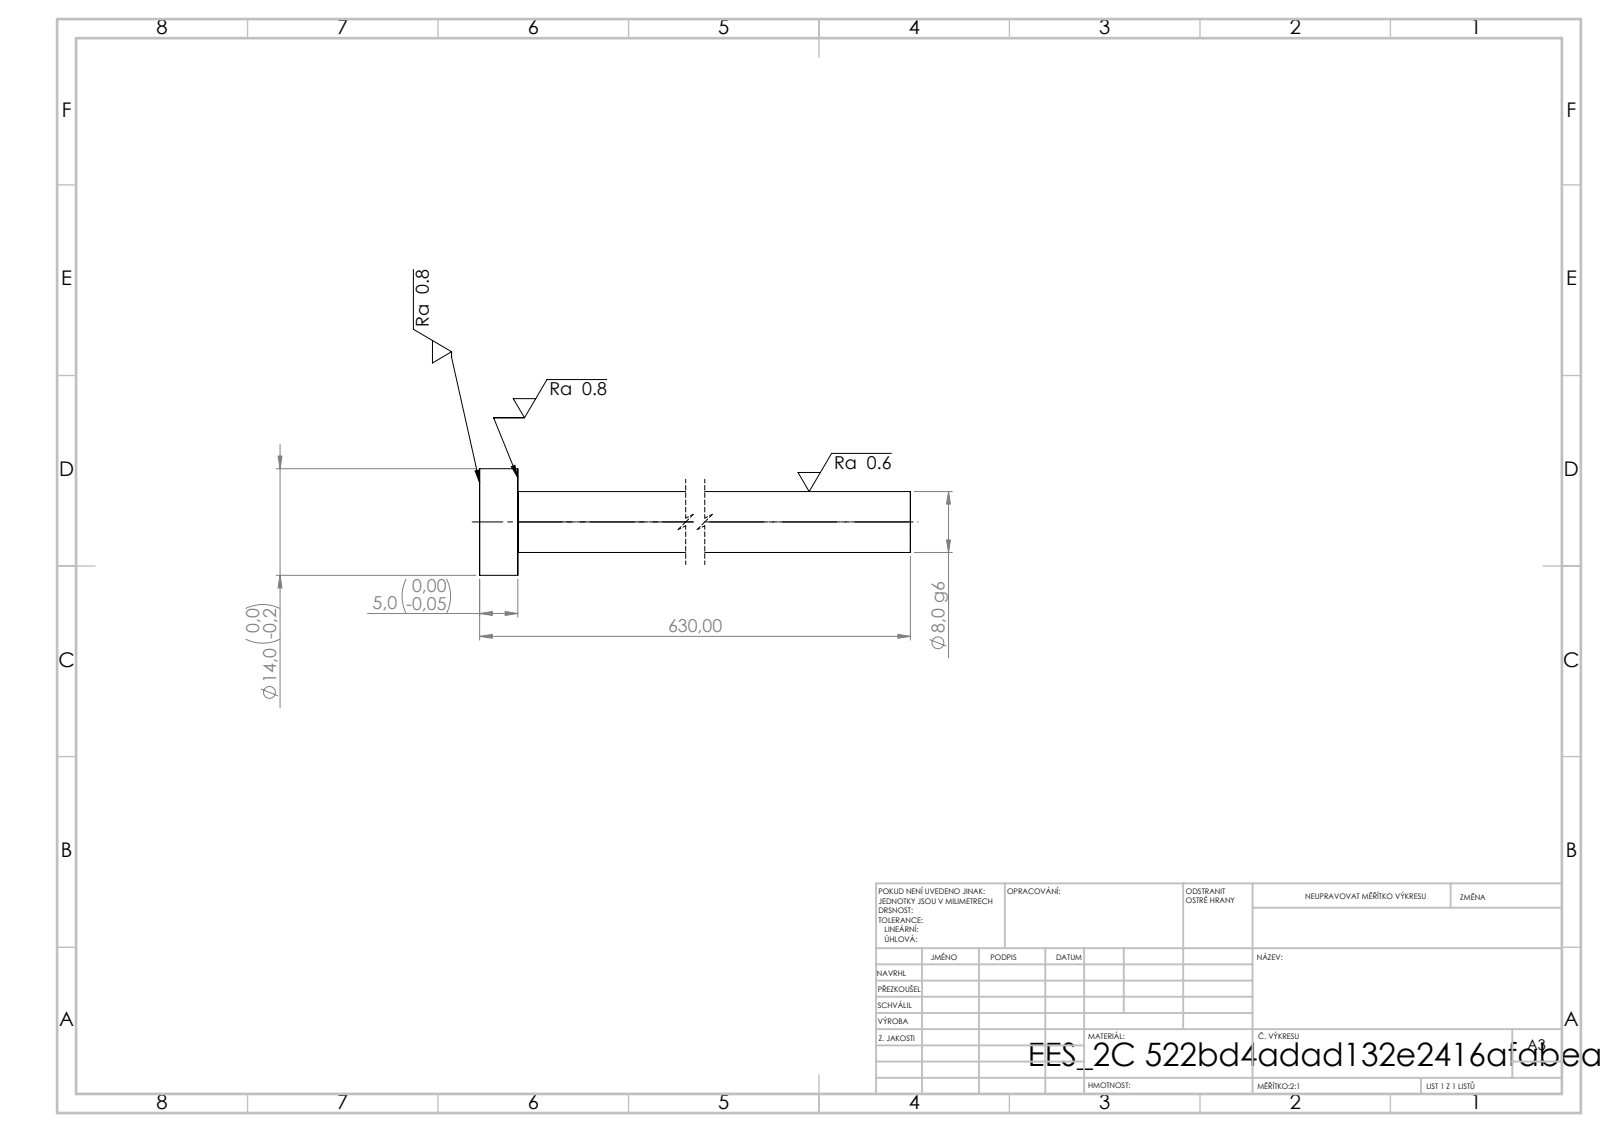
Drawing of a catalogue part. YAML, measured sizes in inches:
step_written_by: "SolidWorks 2019 (CONFIG_CONTROL_DESIGN)"
units: inches
bodies: {solids: 1, faces: 7, planar: 3, cylindrical: 4, other: 0}
overall_size: [24.803, 0.551, 0.551]
volume: 1.964
surface_area: 25.17
round_bosses_or_shafts:
  - {diameter: 0.551, count: 1}
  - {diameter: 0.315, count: 1}
face_to_face_distances: [0.197, 24.803, 24.606]
